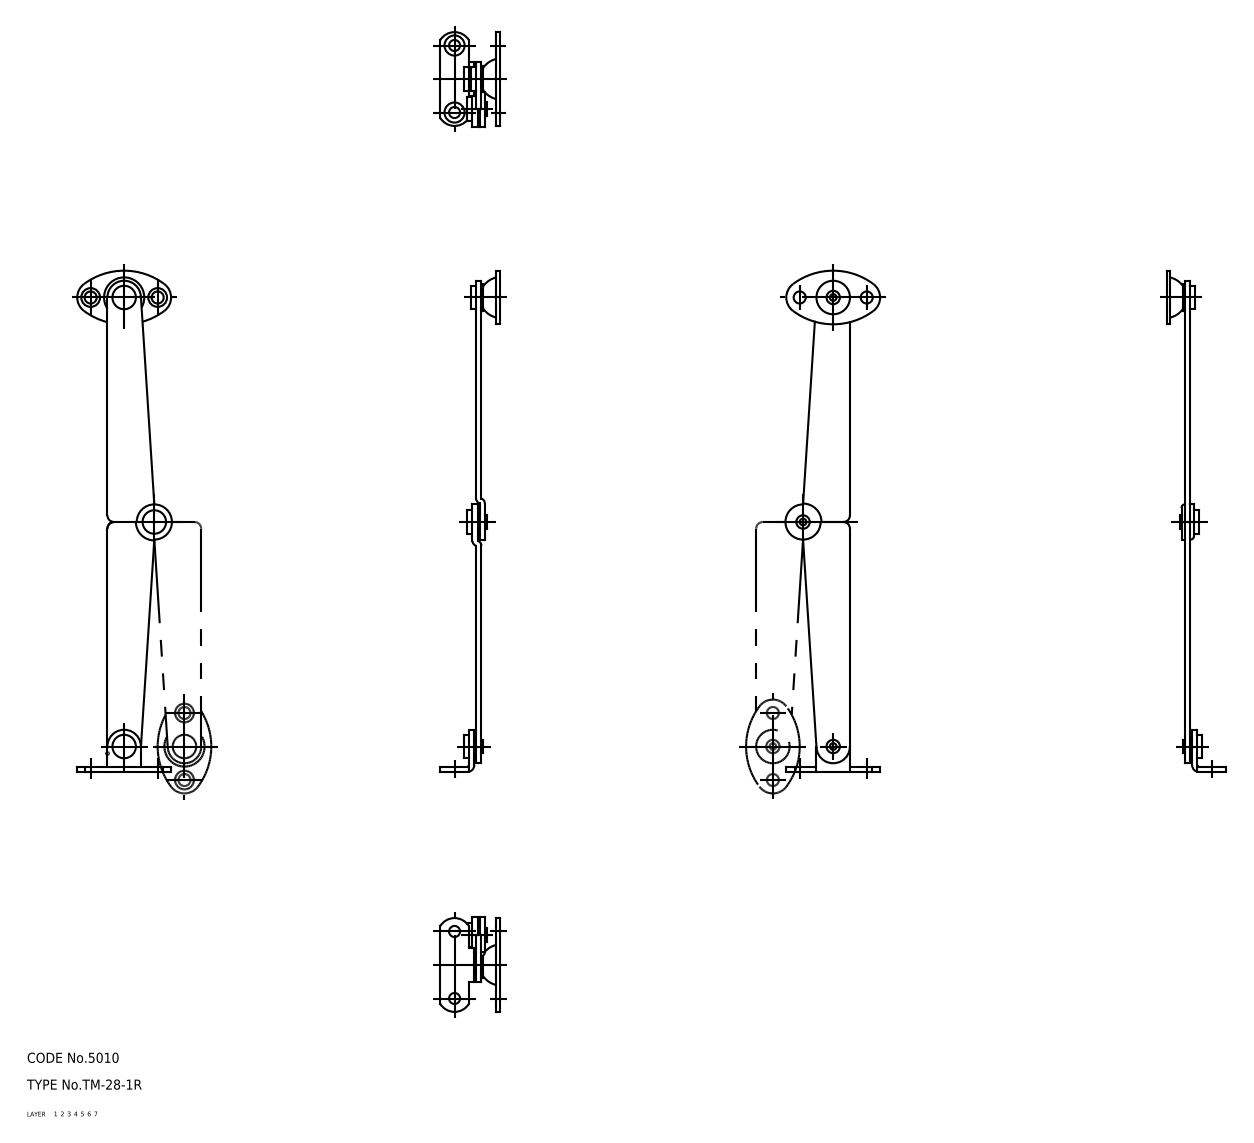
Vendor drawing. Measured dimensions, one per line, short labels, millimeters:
name: washer; rivet; bracket_B; bracket_A (+3 more)
written by: CADfix (AUTOMOTIVE_DESIGN)
unit: mm
bodies: 10 solids, 125 faces (0 planar, 0 cylindrical, 125 other)
size: 149.6 × 28.25 × 17.8
volume: 4 099 mm³; area: 6 762 mm²
